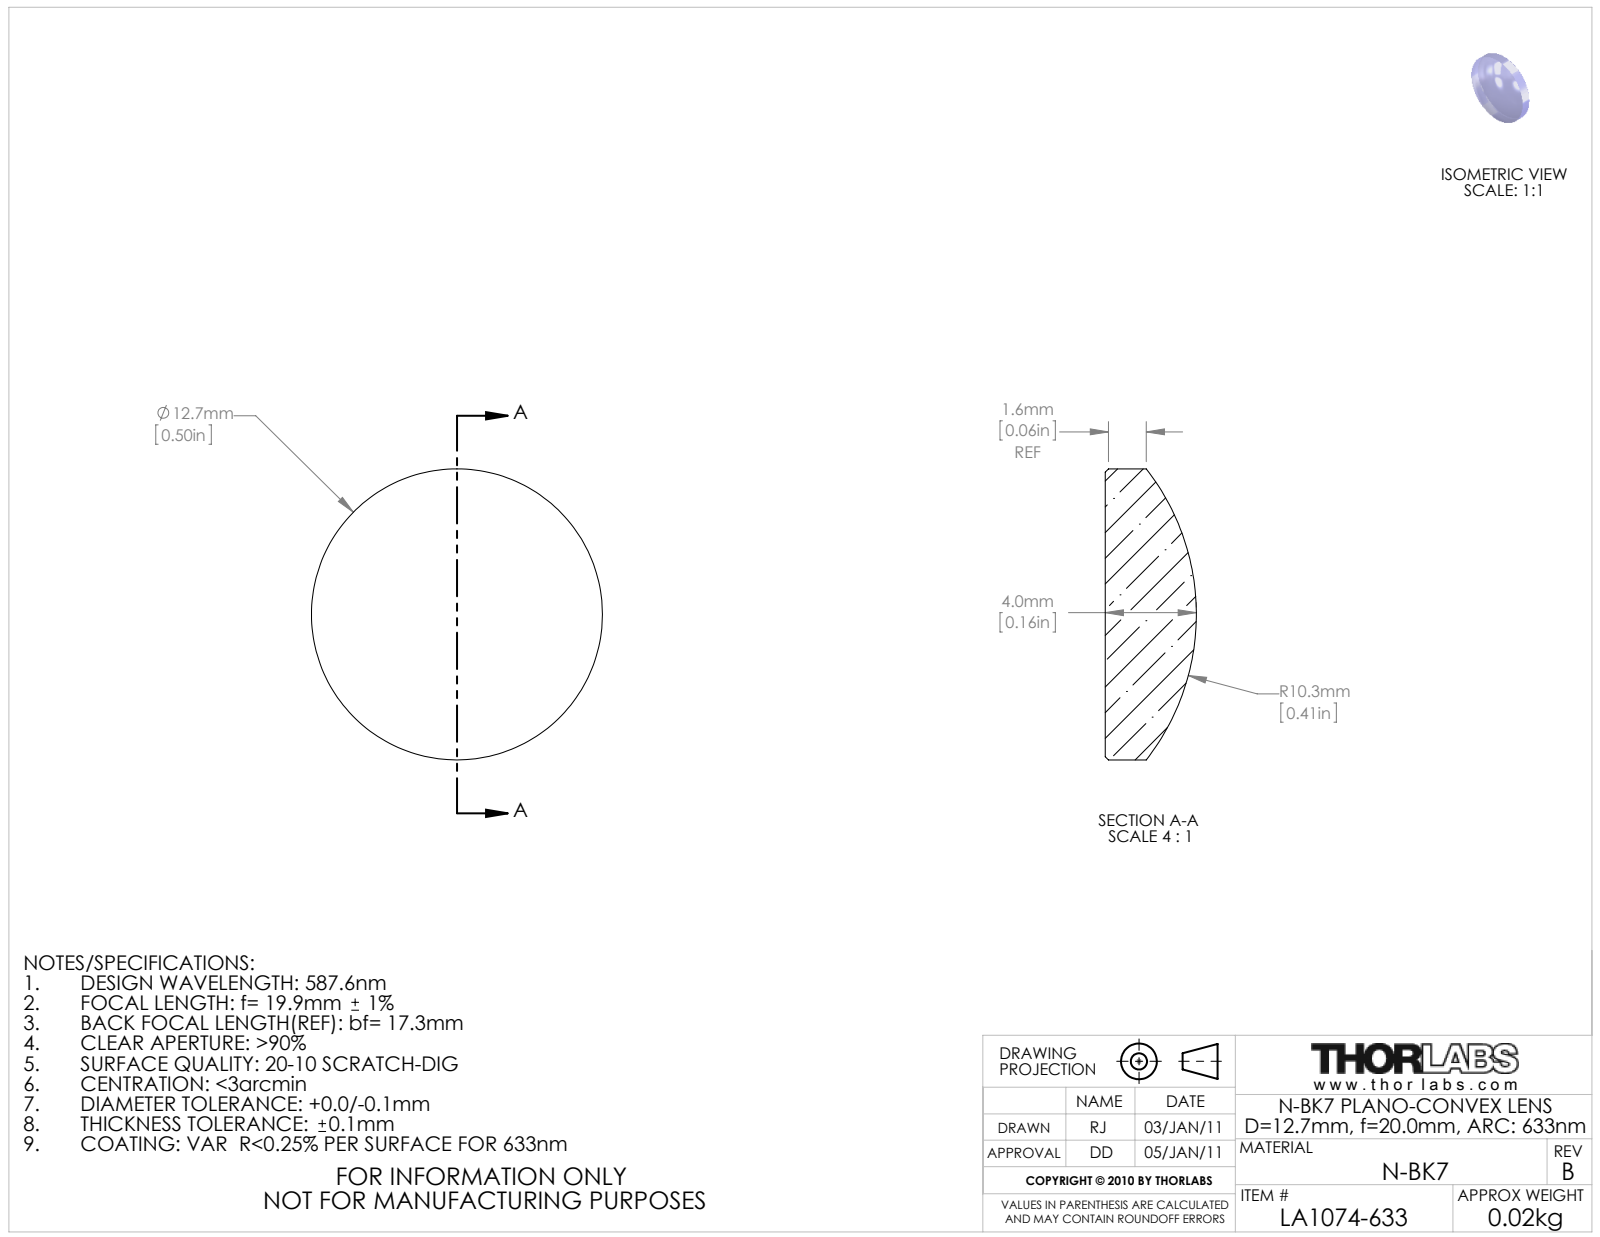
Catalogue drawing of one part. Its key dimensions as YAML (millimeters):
part_name: "21777-E0W"
step_written_by: "SolidWorks 2011 (AUTOMOTIVE_DESIGN)"
units: millimeters
bodies: {solids: 0, faces: 7, planar: 1, cylindrical: 2, other: 4}
overall_size: [12.7, 12.7, 3.98]
round_bosses_or_shafts:
  - {diameter: 12.7, count: 1}
